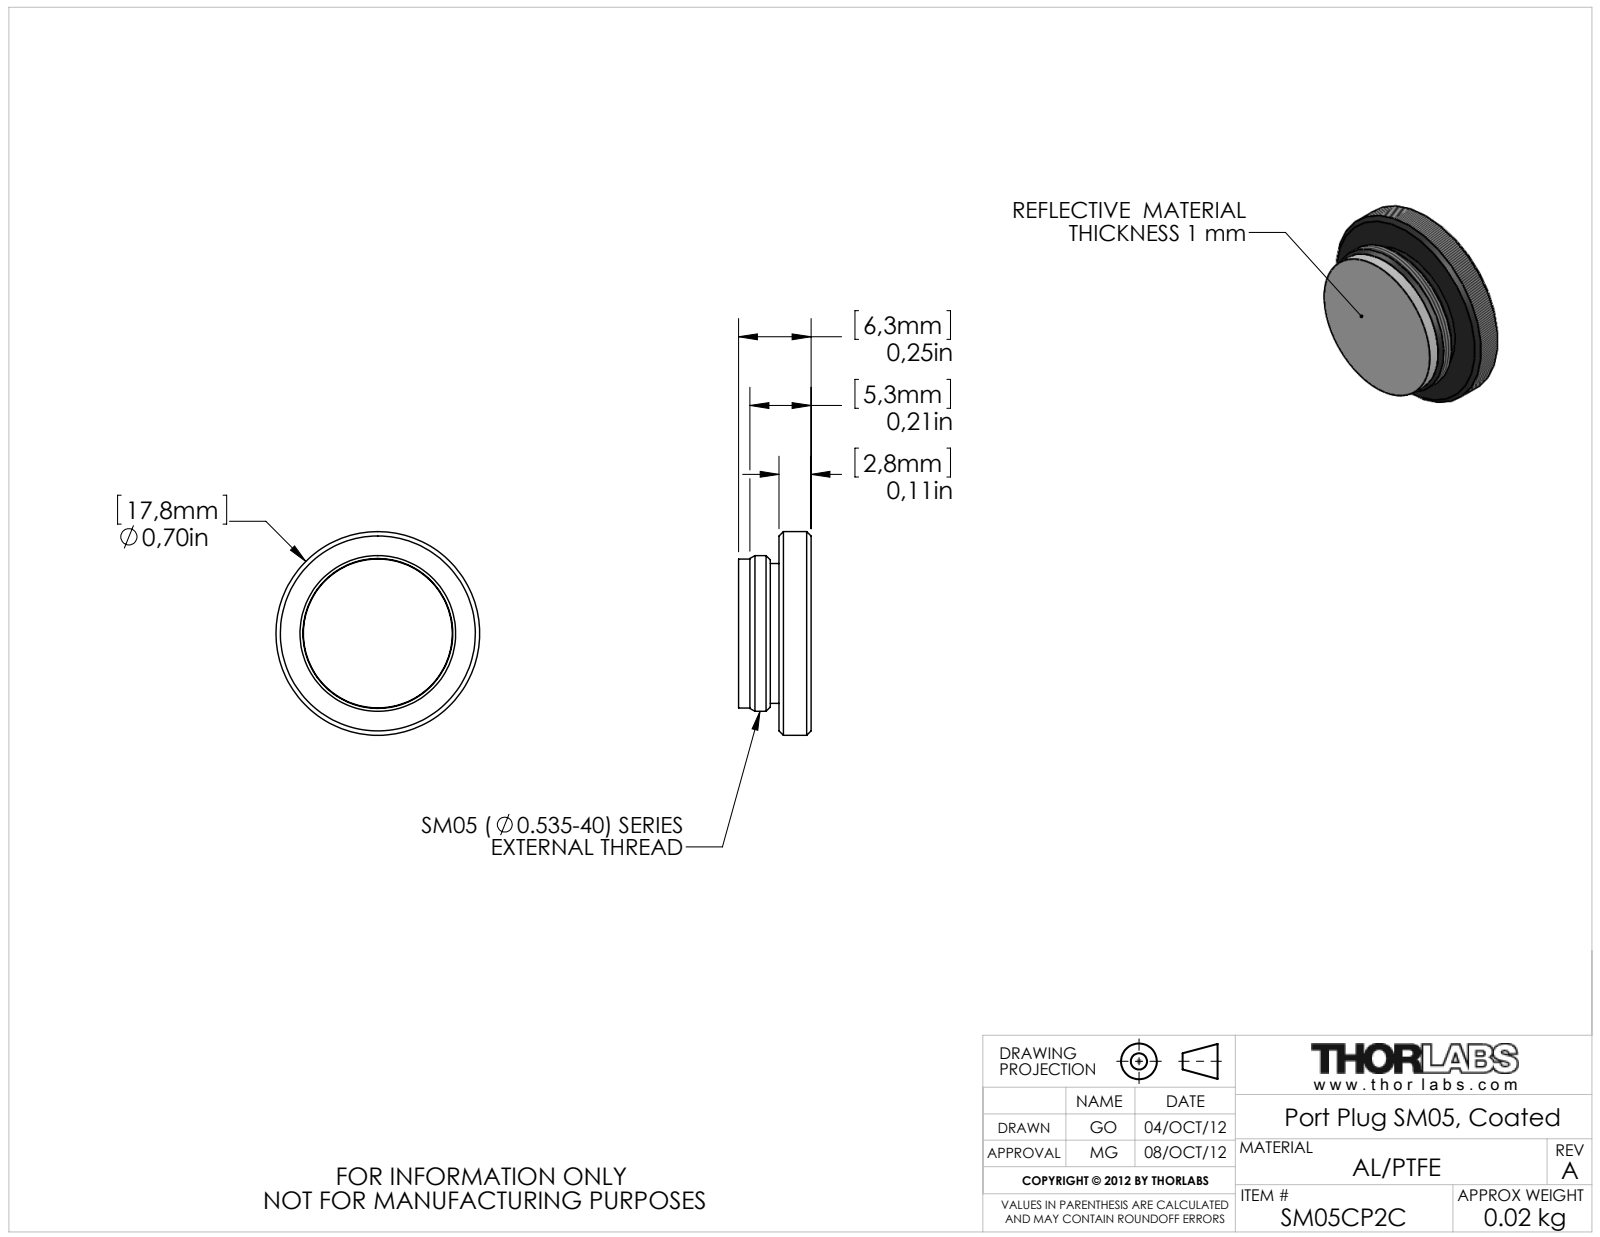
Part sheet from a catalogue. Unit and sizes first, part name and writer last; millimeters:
Units: millimetres
Overall size (bounding box): 17.78 × 17.78 × 6.33
Round bosses / shafts (diameter × count): ⌀17.78 ×1, ⌀13.59 ×1, ⌀13 ×1, ⌀12.19 ×1
Main face-to-face distances: 5.33, 1, 6.33, 3.54, 2.54, 2.79, 2.78, 1.78, 0.76, 3.55
Volume: 1 160 mm³ · Surface area: 1 077 mm²
Bodies: 2 solids, 22 faces (6 planar, 8 cylindrical, 8 other)
Part name (STEP PRODUCT): 25046-E0W; SM05CP2-Solidworks; PTFE Disc 13mm
STEP written by: SolidWorks 2012 (CONFIG_CONTROL_DESIGN)
